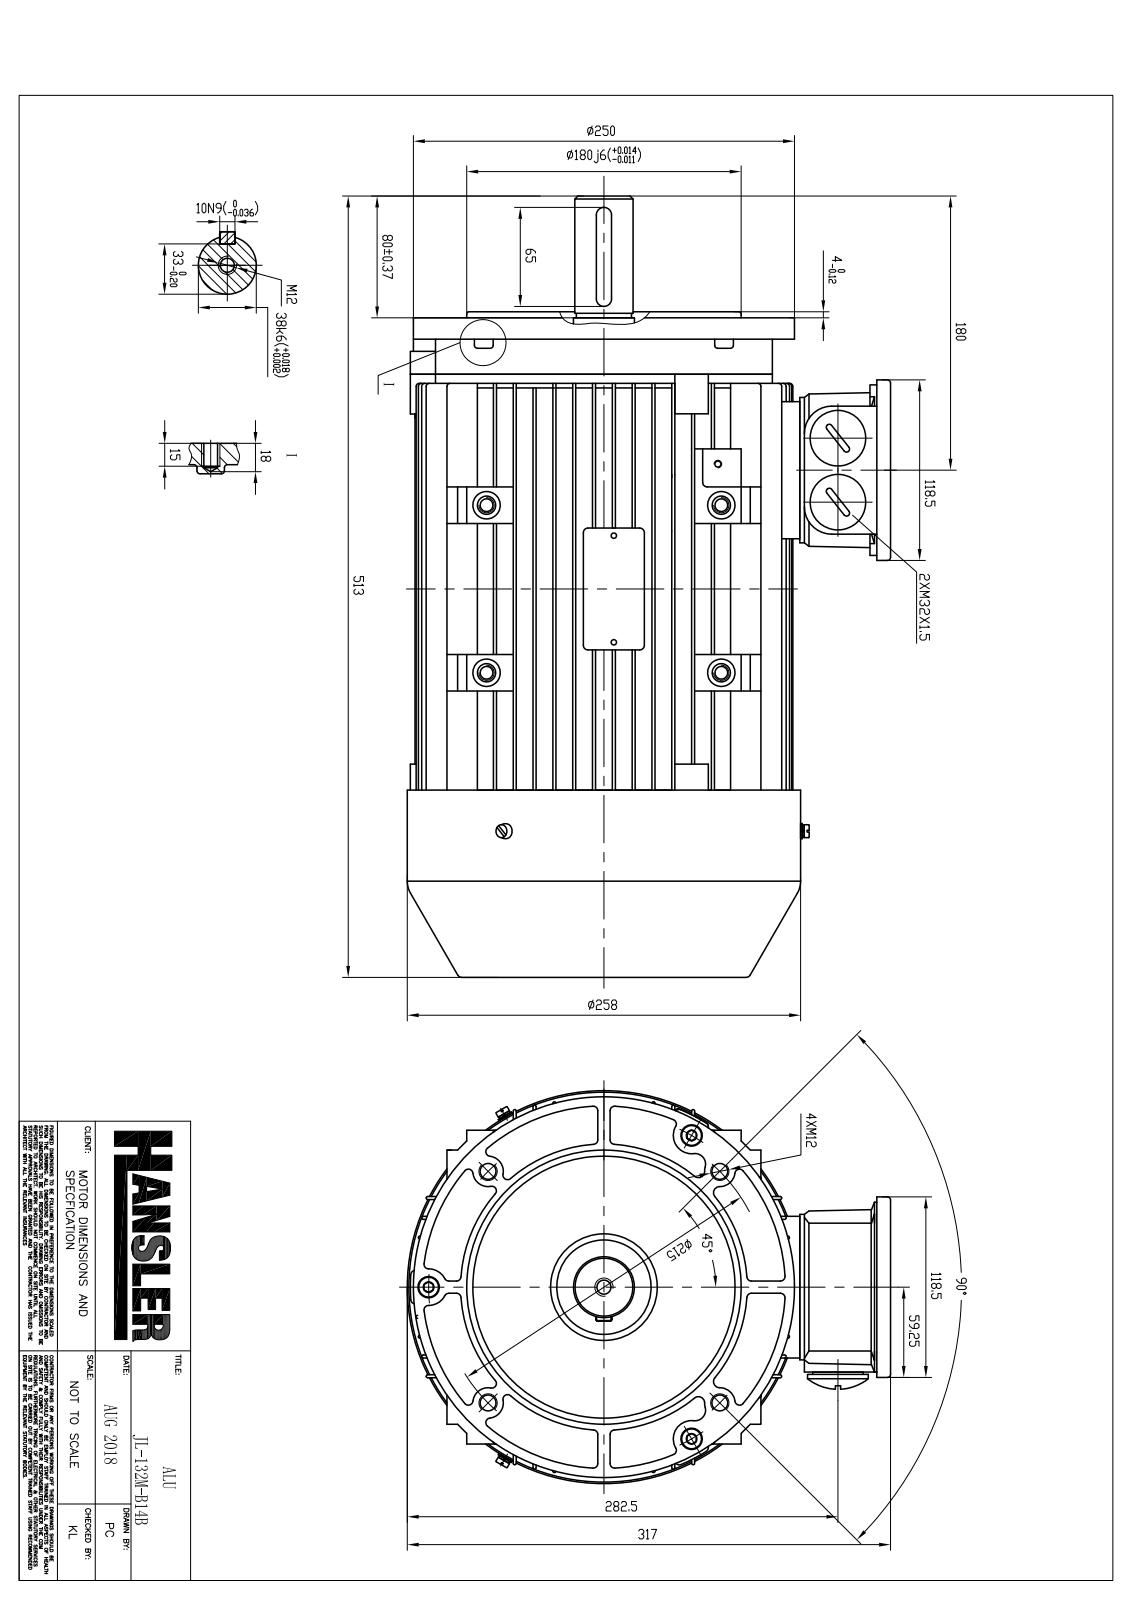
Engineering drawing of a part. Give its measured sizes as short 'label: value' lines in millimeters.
name: JL-132M-B14B
written by: SIEMENS PLM Software NX 12.0 (AP203_CONFIGURATION_CONTROLLED_3D_DESIGN_OF_MECHANICAL_PARTS_AND_ASSEMBLIES_MIM_LF)
unit: mm
bodies: 47 solids, 4989 faces (2946 planar, 1629 cylindrical, 414 other)
size: 513 × 320 × 263.33
volume: 3 634 000 mm³; area: 1 810 000 mm²
holes: 23× ⌀5, 14× ⌀10, 10× ⌀5.8, 8× ⌀18, 4× ⌀4.8, 4× ⌀5.25, 4× ⌀5.3, 4× ⌀8, 4× ⌀12, 3× ⌀8.39, 3× ⌀9.1, 3× ⌀14
bosses: 8× ⌀12, 8× ⌀4.48, 6× ⌀4.8, 4× ⌀16, 4× ⌀10, 4× ⌀7.85, 3× ⌀13, 3× ⌀12.59
rounds: 816× R0.5, 58× R3, 38× R2, 34× R1, 34× R4, 18× R2.5, 10× R6, 9× R5
face distances: 13, 2, 26, 91, 11, 104, 15, 78, 39, 24
hole spacings: 40.23, 57.6, 61.1, 78.63, 84.34, 56.94, 17.68, 18
